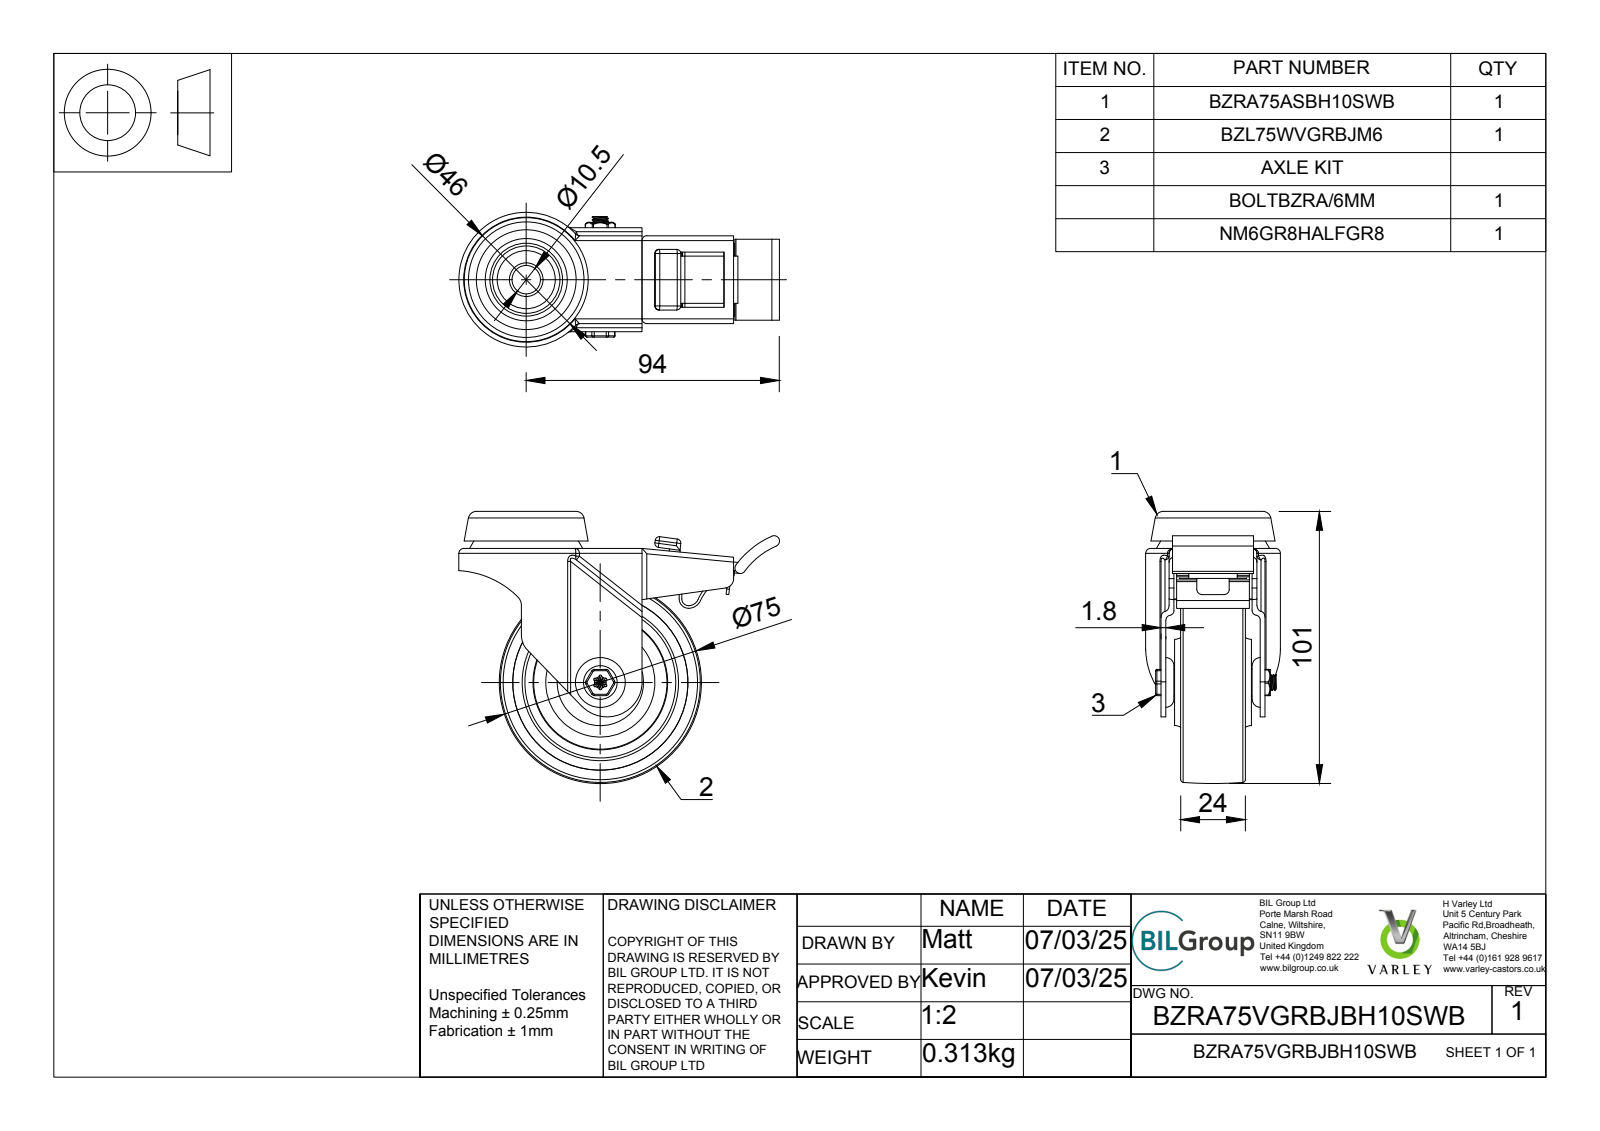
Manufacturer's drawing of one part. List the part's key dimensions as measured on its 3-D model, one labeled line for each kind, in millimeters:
Part name (STEP PRODUCT): BZRA75VGRBJBH10SWB v3; BZRA75ASBH10SWB v1; ZINC PLATED PRESSED STEEL HEAD; ZINC PLATED PRESSED STEEL FORKS (+7 more)
STEP written by: Autodesk Translation Framework v13.20.0.188 (AP242_MANAGED_MODEL_BASED_3D_ENGINEERING_MIM_LF)
Units: millimetres
Bodies: 22 solids, 615 faces (257 planar, 194 cylindrical, 164 other)
Overall size (bounding box): 119 × 101 × 50
Volume: 108 362 mm³ · Surface area: 86 078 mm²
Round holes (diameter × count): ⌀6 ×1, ⌀6.2 ×1, ⌀6.5 ×1, ⌀8.5 ×1, ⌀10.5 ×1, ⌀10.55 ×1, ⌀10.56 ×1, ⌀11.2 ×1, ⌀12.74 ×1, ⌀16 ×1, ⌀18.3 ×1, ⌀19.2 ×1
Round bosses / shafts (diameter × count): ⌀56 ×1, ⌀39 ×1, ⌀30.75 ×1, ⌀18.7 ×1, ⌀18.32 ×1, ⌀18 ×1, ⌀14.76 ×1, ⌀14 ×1
Partial cylindrical surfaces — rounded edges, fillets, slot ends (radius × count): R1 ×22, R1.8 ×22, R0.5 ×12, R1.5 ×11, R0.9 ×10, R0.4 ×6, R2 ×5, R3.5 ×2
Main face-to-face distances: 1.8, 13.75, 33.8, 10.25, 3, 12.75, 2, 6.25, 24.25, 3.25
